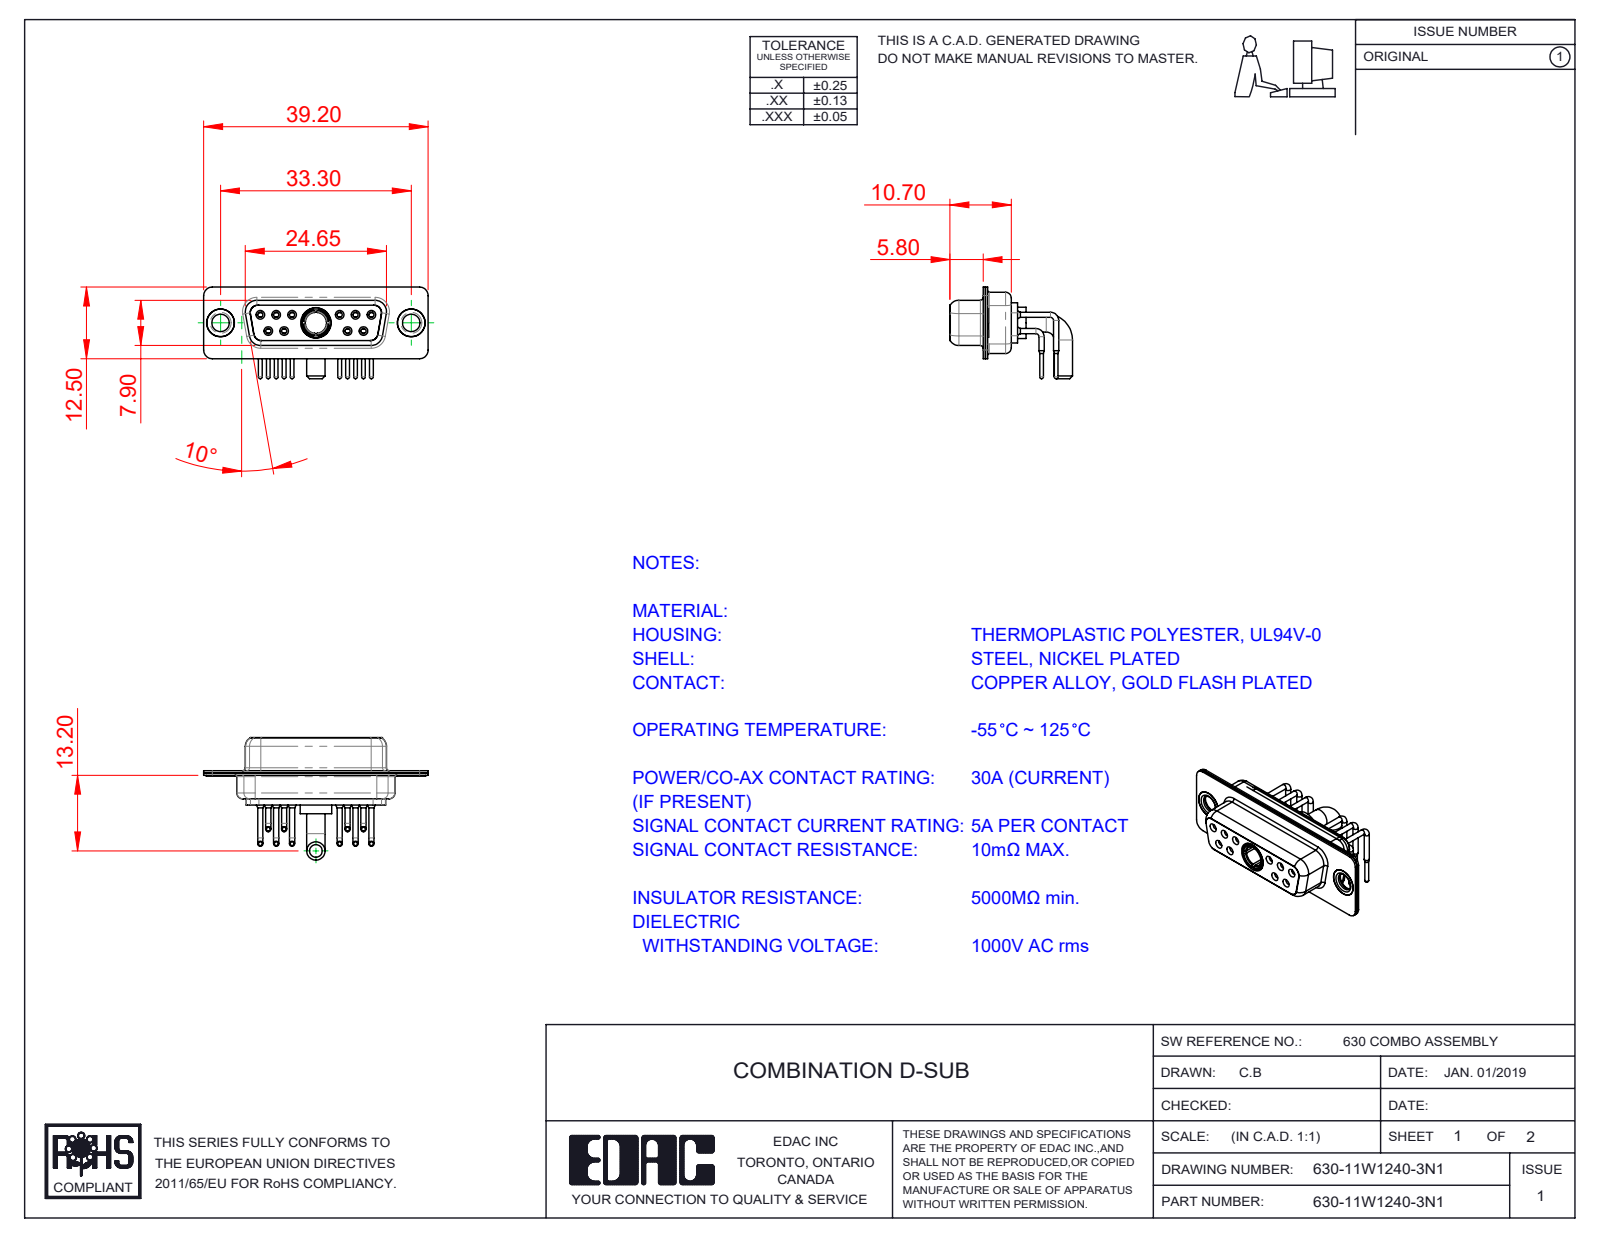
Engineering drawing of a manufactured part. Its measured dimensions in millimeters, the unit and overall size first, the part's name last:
Units: millimetres
Overall size (bounding box): 39.2 × 21.4 × 16
Round holes (diameter × count): ⌀0.9 ×10, ⌀1.1 ×10, ⌀1.5 ×10, ⌀2 ×10, ⌀1.7 ×6, ⌀1.6 ×4, ⌀4.85 ×3, ⌀3.05 ×2, ⌀4 ×2, ⌀4.05 ×2, ⌀3.7 ×1, ⌀5.3 ×1
Round bosses / shafts (diameter × count): ⌀0.9 ×10, ⌀0.65 ×10, ⌀1.6 ×6, ⌀5 ×2, ⌀4.95 ×2, ⌀4.8 ×2, ⌀3.55 ×2, ⌀3.2 ×2
Partial cylindrical surfaces — rounded edges, fillets, slot ends (radius × count): R1.5 ×16, R1.35 ×12, R2 ×12, R1.6 ×8, R0.25 ×4, R0.5 ×4, R0.6 ×4, R0.65 ×4
Main face-to-face distances: 0.4, 1.4, 0.45, 8.45, 1.8, 8.9, 6.2, 0.8, 7.05, 1.85
Hole centre spacings: 3.16, 2.77, 13.85, 11.08, 16.62, 5.03, 5.04, 5.54
Volume: 2 597 mm³ · Surface area: 6 145 mm²
Bodies: 17 solids, 861 faces (246 planar, 376 cylindrical, 239 other)
Part name (STEP PRODUCT): Power Socket_30A RA; 630Combo Shell Front_15 Contacts; 630Combo Contact Row 1; 630-11W1240-3N1 (+4 more)
STEP written by: SolidWorks 2020 (CONFIG_CONTROL_DESIGN)
